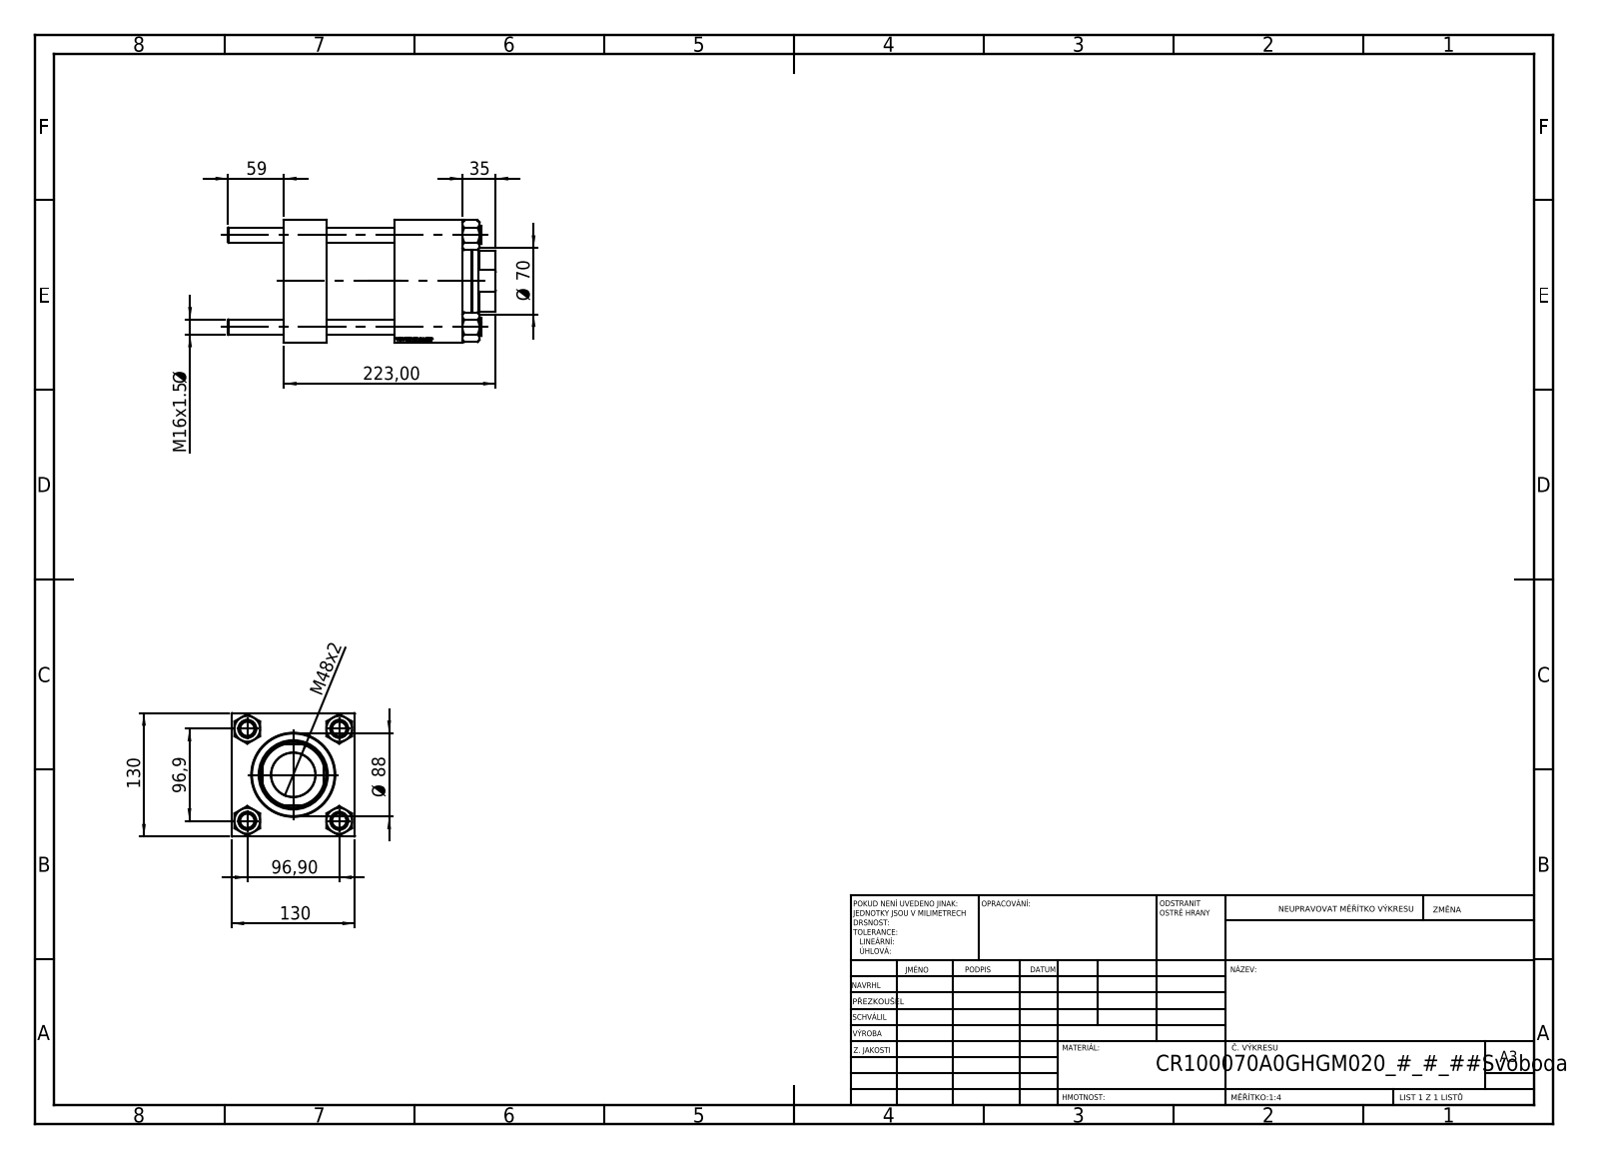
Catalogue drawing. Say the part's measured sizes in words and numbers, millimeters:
The part is named "V215CR_VCP; V215CR_BODY_A; NUT_M5; V215_VC_A (+1 more)". Its 3-D file was written by "SolidWorks 2019 (CONFIG_CONTROL_DESIGN)". It is 11 solids with 1182 faces: 568 planar, 78 cylindrical and 536 other. Overall it measures 282 by 130 by 130 millimeters. Its volume is 2 655 000 cubic millimeters and its surface area 368 455 square millimeters. Round holes: 4 of diameter 16, 2 of diameter 7, 2 of diameter 26.44, 2 of diameter 35, 1 of diameter 46.5, 1 of diameter 70, 1 of diameter 73, 1 of diameter 76, 1 of diameter 85.5, 1 of diameter 100. Round bosses or shafts: 4 of diameter 19, 1 of diameter 106, 1 of diameter 88. Partial cylindrical surfaces (rounded edges, fillets, slot ends): 1 of radius 34. The main face-to-face distances are 130, 45, 188, 143, 116, 71, 72, 92, 20, 96. The hole center spacings are 68.52, 96.9, 137.04, 118.5.
